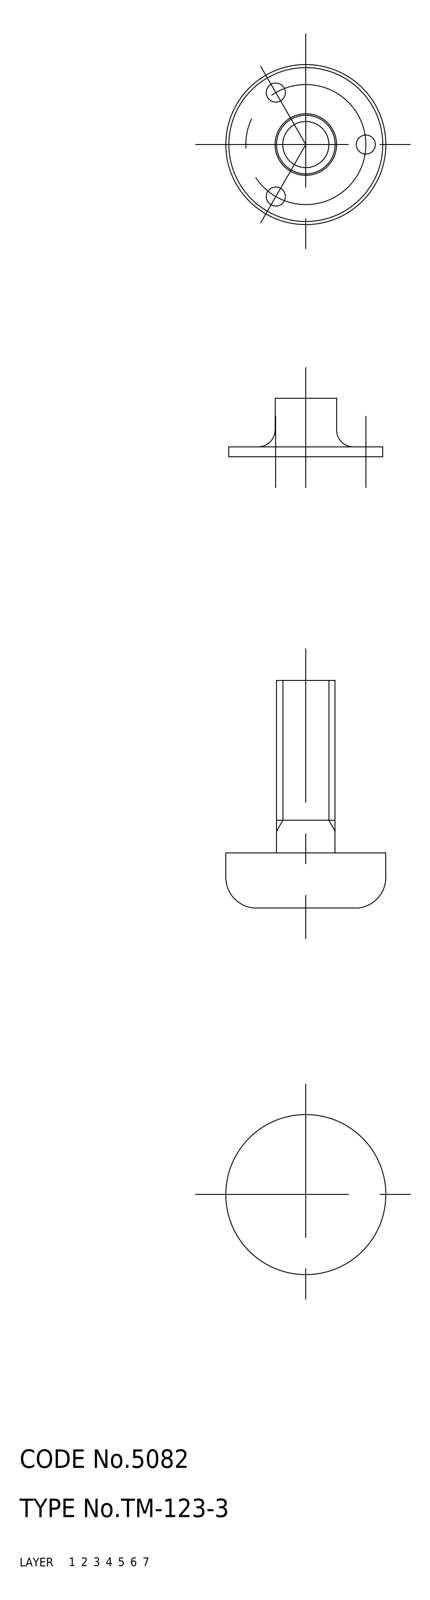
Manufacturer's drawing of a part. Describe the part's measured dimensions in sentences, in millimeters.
The part is named "nut; foot; bolt; TM_123_3_14496_36". Its 3-D file was written by "CADfix (AUTOMOTIVE_DESIGN)". It is 3 solids with 32 faces: 0 planar, 0 cylindrical and 32 other. Overall it measures 37 by 26 by 26 millimeters. Its volume is 7 128 cubic millimeters and its surface area 4 218 square millimeters.
